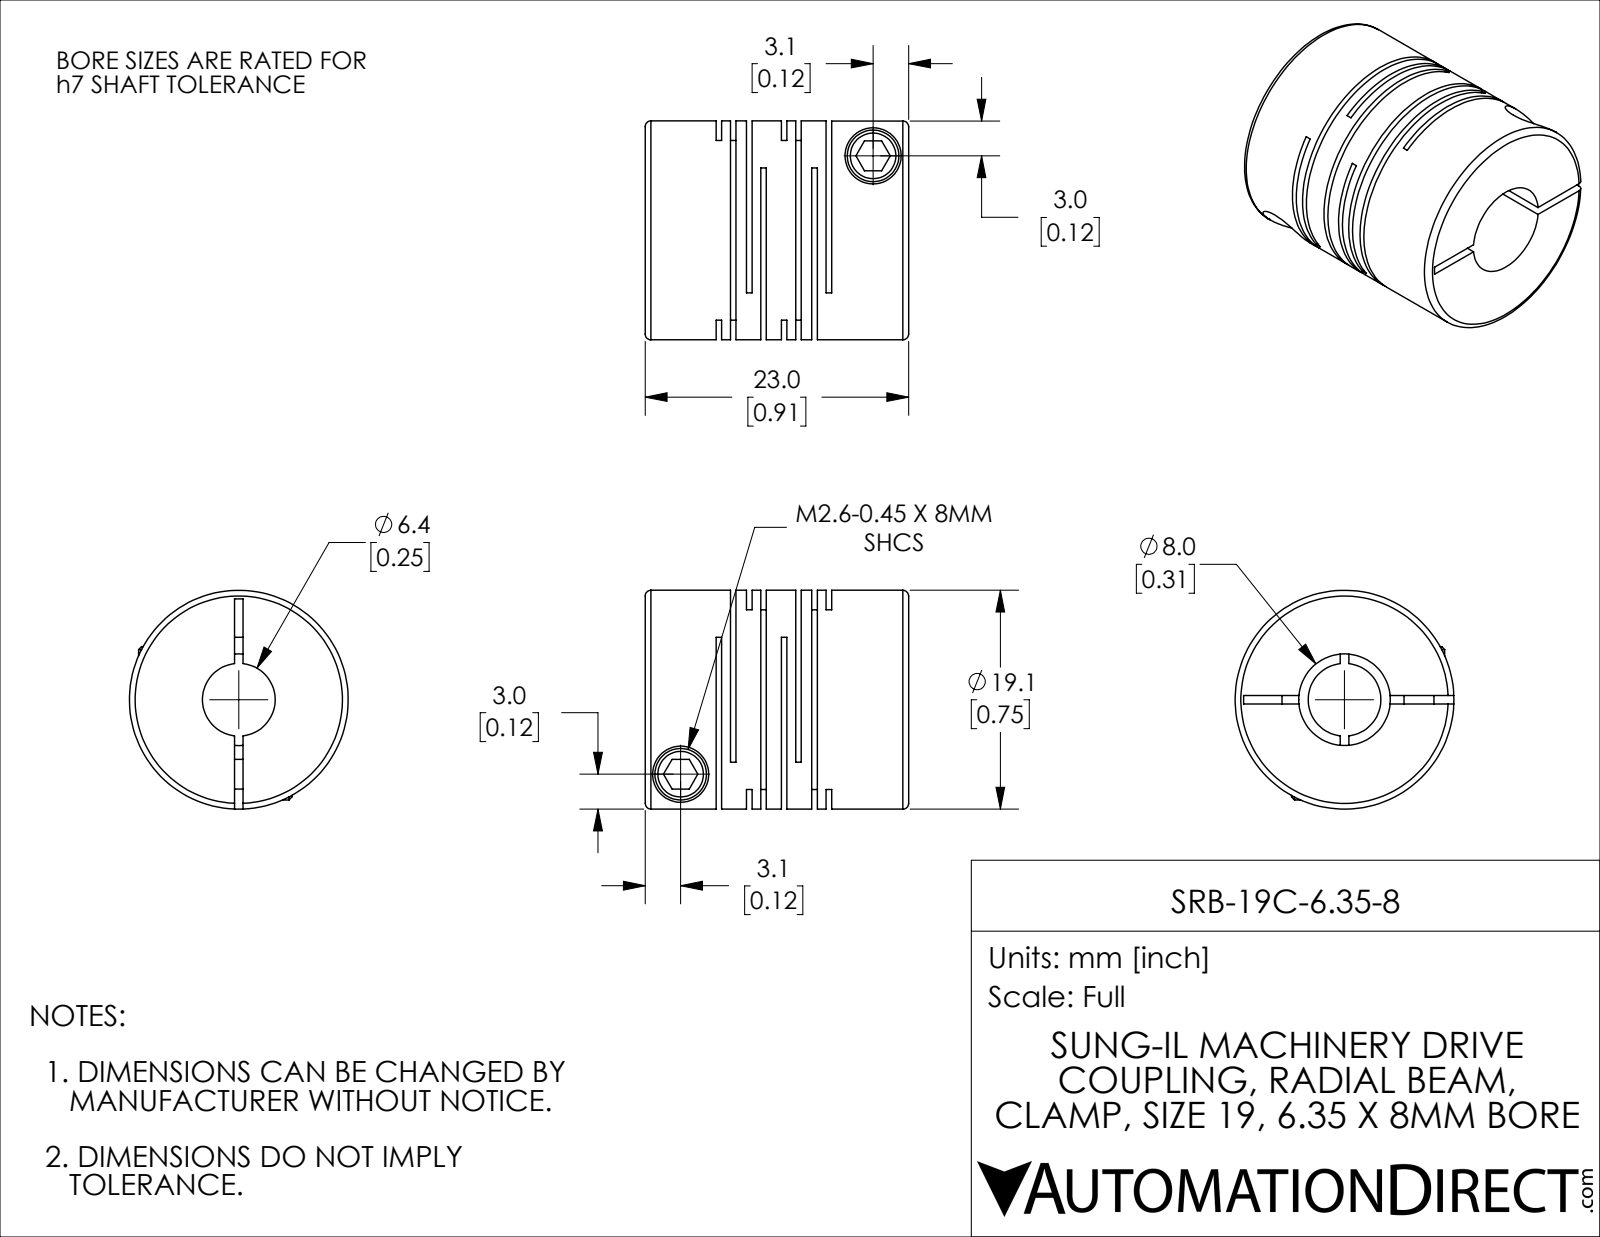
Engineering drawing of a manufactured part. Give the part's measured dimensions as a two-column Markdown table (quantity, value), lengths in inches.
| quantity | value |
| --- | --- |
| part name | SRB-19C-6.35-8 |
| STEP written by | SolidWorks 2021 (CONFIG_CONTROL_DESIGN) |
| units | inches |
| bodies | 1 solid, 114 faces (60 planar, 42 cylindrical, 12 other) |
| overall size | 0.906 × 0.752 × 0.752 |
| volume | 0.28 in³ |
| surface area | 8.861 in² |
| round holes (diameter × count) | 0.102 × 2, 0.193 × 2, 0.25 × 1, 0.315 × 1 |
| round bosses / shafts (diameter × count) | 0.177 × 2, 0.752 × 1 |
| main face-to-face distances | 0.224, 0.019, 0.049, 0.104, 0.085, 0.12, 0.206, 0.175, 0.03, 0.055 |
